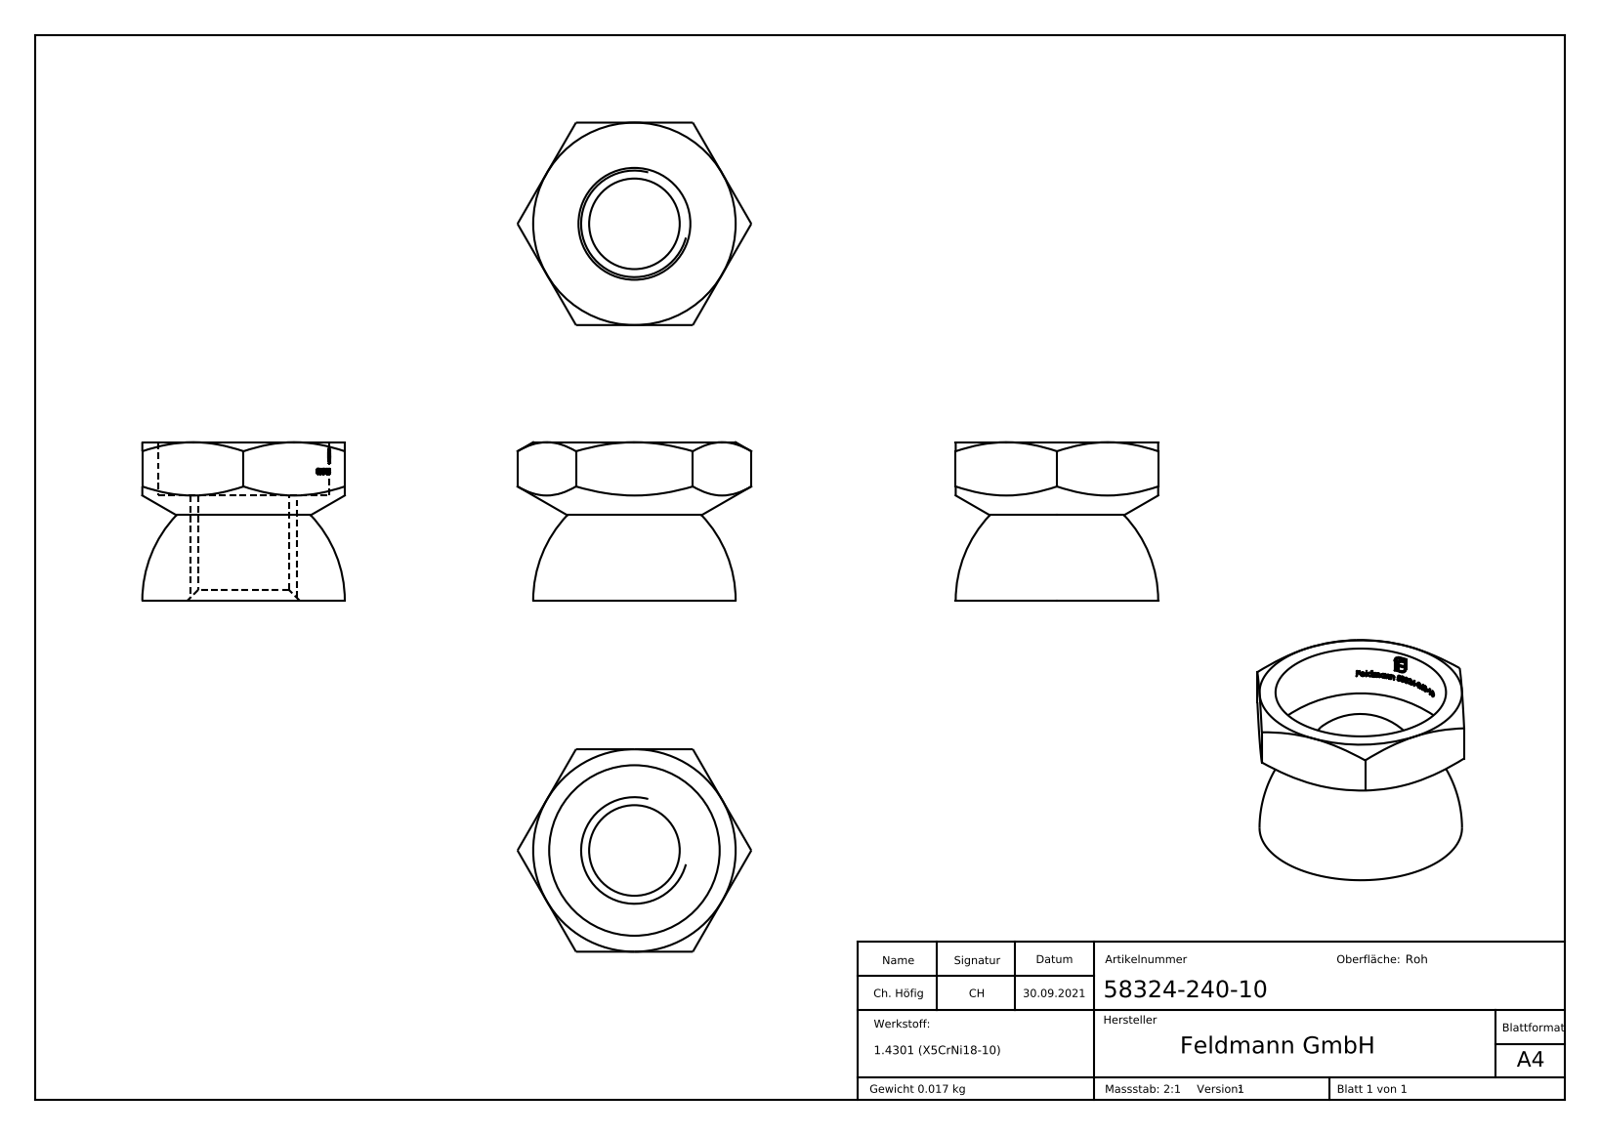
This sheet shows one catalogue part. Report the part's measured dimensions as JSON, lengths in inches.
{"part_name": "58324-240-10", "step_written_by": "SolidWorks 2018 (CONFIG_CONTROL_DESIGN)", "units": "inches", "bodies": {"solids": 1, "faces": 324, "planar": 146, "cylindrical": 32, "other": 146}, "overall_size": [0.864, 0.748, 0.585], "volume_in3": 0.133, "surface_area_in2": 3.049, "round_holes": [[0.335, 1], [0.63, 1]], "partial_cylinders_radius": [[0.319, 1]], "face_to_face_distances": [0.748, 0.388, 0.585, 0.197, 0.079, 0.118, 0.032, 0.019, 0.18, 0.097]}
